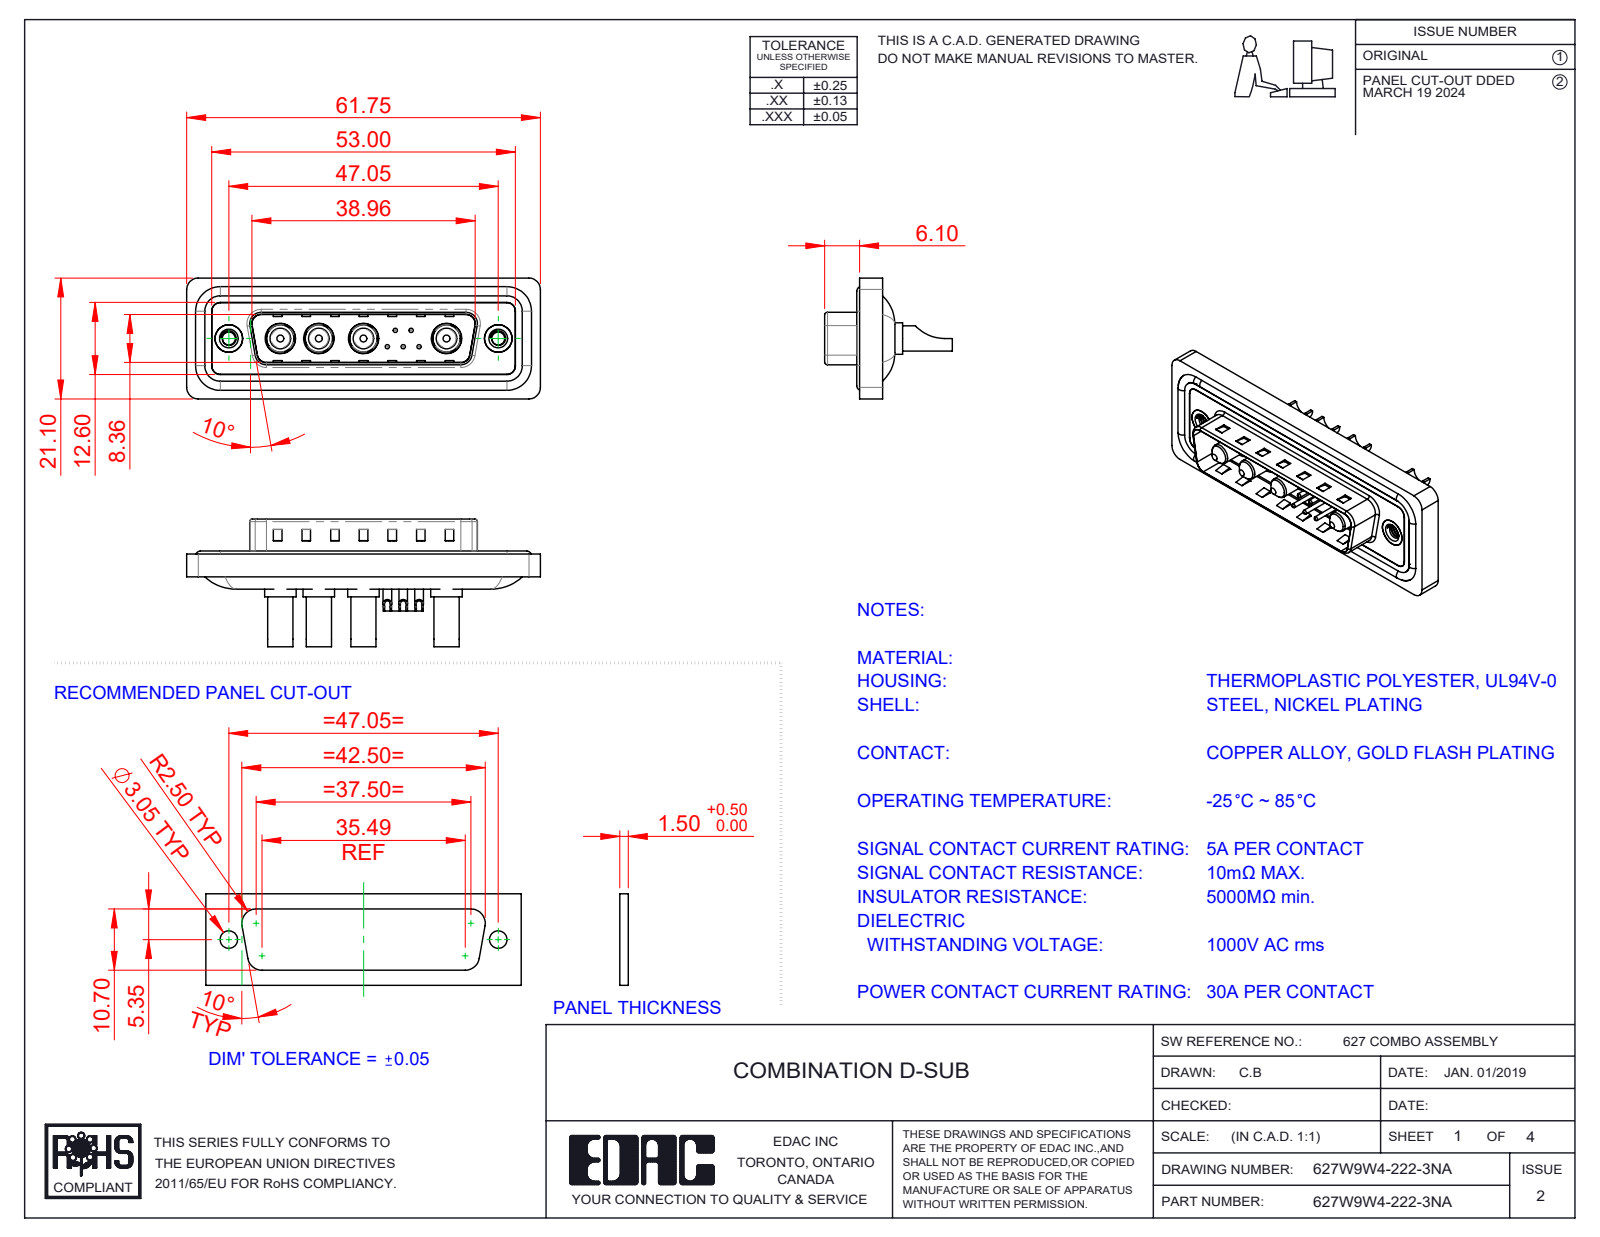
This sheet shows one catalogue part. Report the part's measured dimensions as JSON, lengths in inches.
{"part_name": "627Combo Contact Row 2_22; 627Combo Contact Row 1_22; 627W9W4-222-3NA; 627Combo Housing_9W4 (+5 more)", "step_written_by": "SolidWorks 2023 (CONFIG_CONTROL_DESIGN)", "units": "inches", "bodies": {"solids": 20, "faces": 846, "planar": 306, "cylindrical": 358, "other": 182}, "overall_size": [2.431, 0.878, 0.831], "volume_in3": 0.458, "surface_area_in2": 19.07, "round_holes": [[0.03, 5], [0.039, 5], [0.063, 5], [0.079, 5], [0.138, 4], [0.191, 4], [0.209, 4], [0.089, 2], [0.157, 2], [0.189, 2], [0.197, 2]], "round_bosses_or_shafts": [[0.059, 5], [0.217, 4], [0.205, 4], [0.187, 4], [0.173, 4], [0.148, 4], [0.142, 4], [0.063, 4]], "partial_cylinders_radius": [[0.059, 22], [0.079, 18], [0.02, 8], [0.063, 8], [0.039, 6], [0.01, 4], [0.024, 4], [0.026, 4]], "face_to_face_distances": [0.016, 0.059, 0.043, 0.02, 0.063, 0.122, 0.114, 0.032, 0.377, 0.222], "hole_center_spacings": [0.124, 0.109, 0.198, 0.571, 0.109, 0.173, 0.174, 0.197]}
